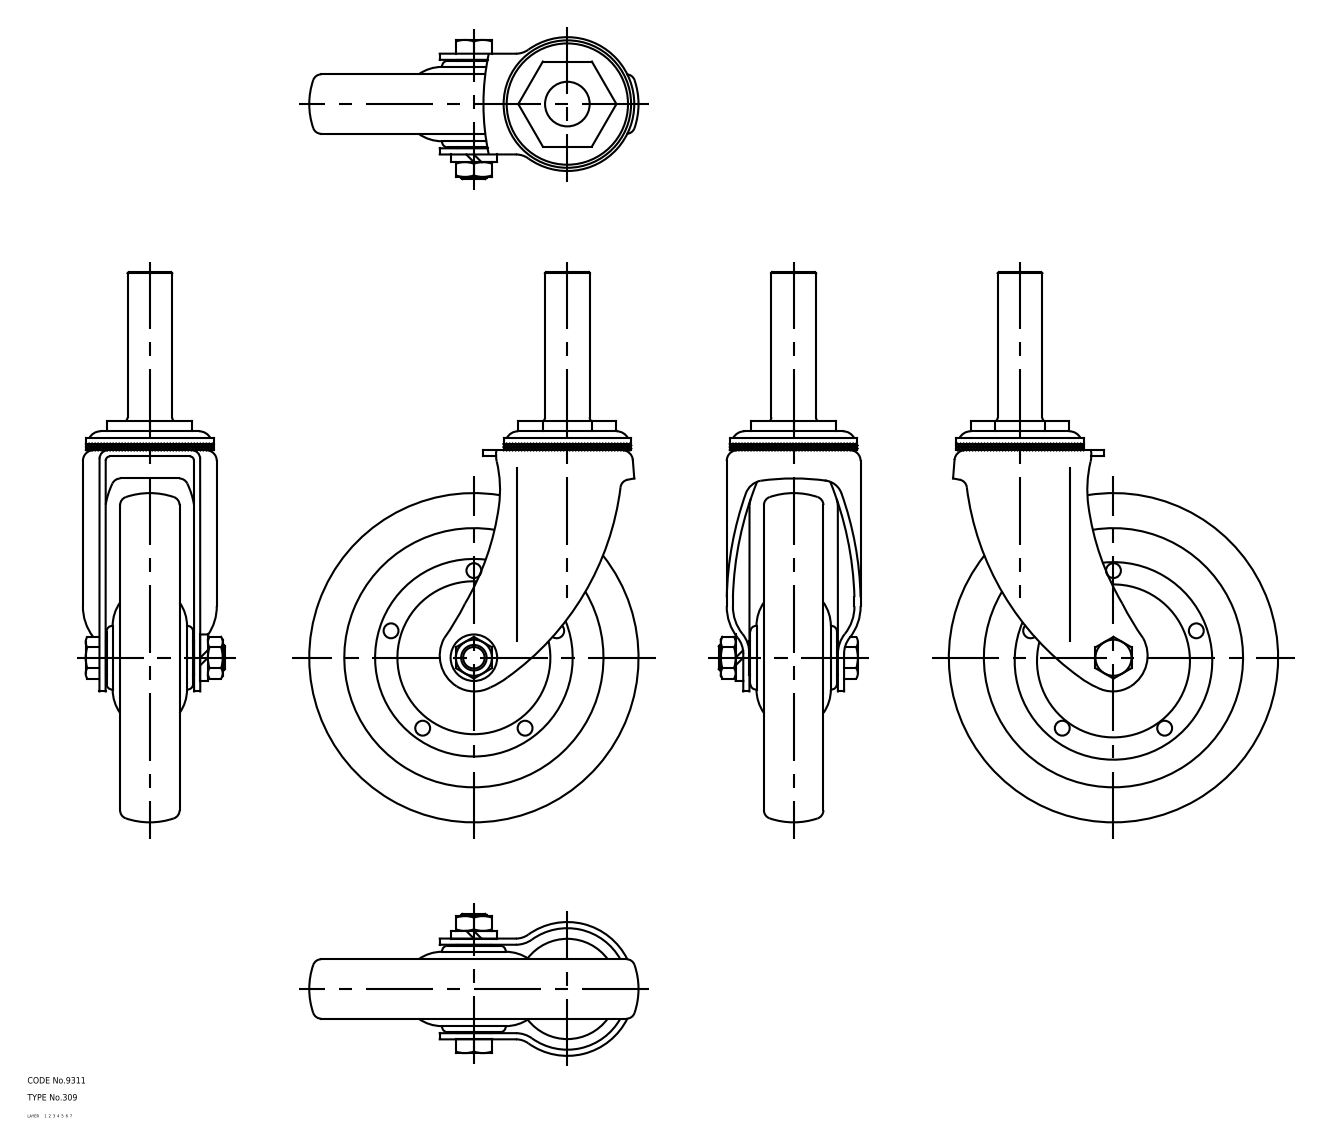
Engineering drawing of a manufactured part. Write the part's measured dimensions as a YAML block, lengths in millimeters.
part_name: "67131144; 67131157; 67131170; 67131183"
step_written_by: "CADfix (AUTOMOTIVE_DESIGN)"
units: millimeters
bodies: {solids: 4, faces: 229, planar: 0, cylindrical: 0, other: 229}
overall_size: [259, 155, 66.78]
volume: 553700
surface_area: 100435
